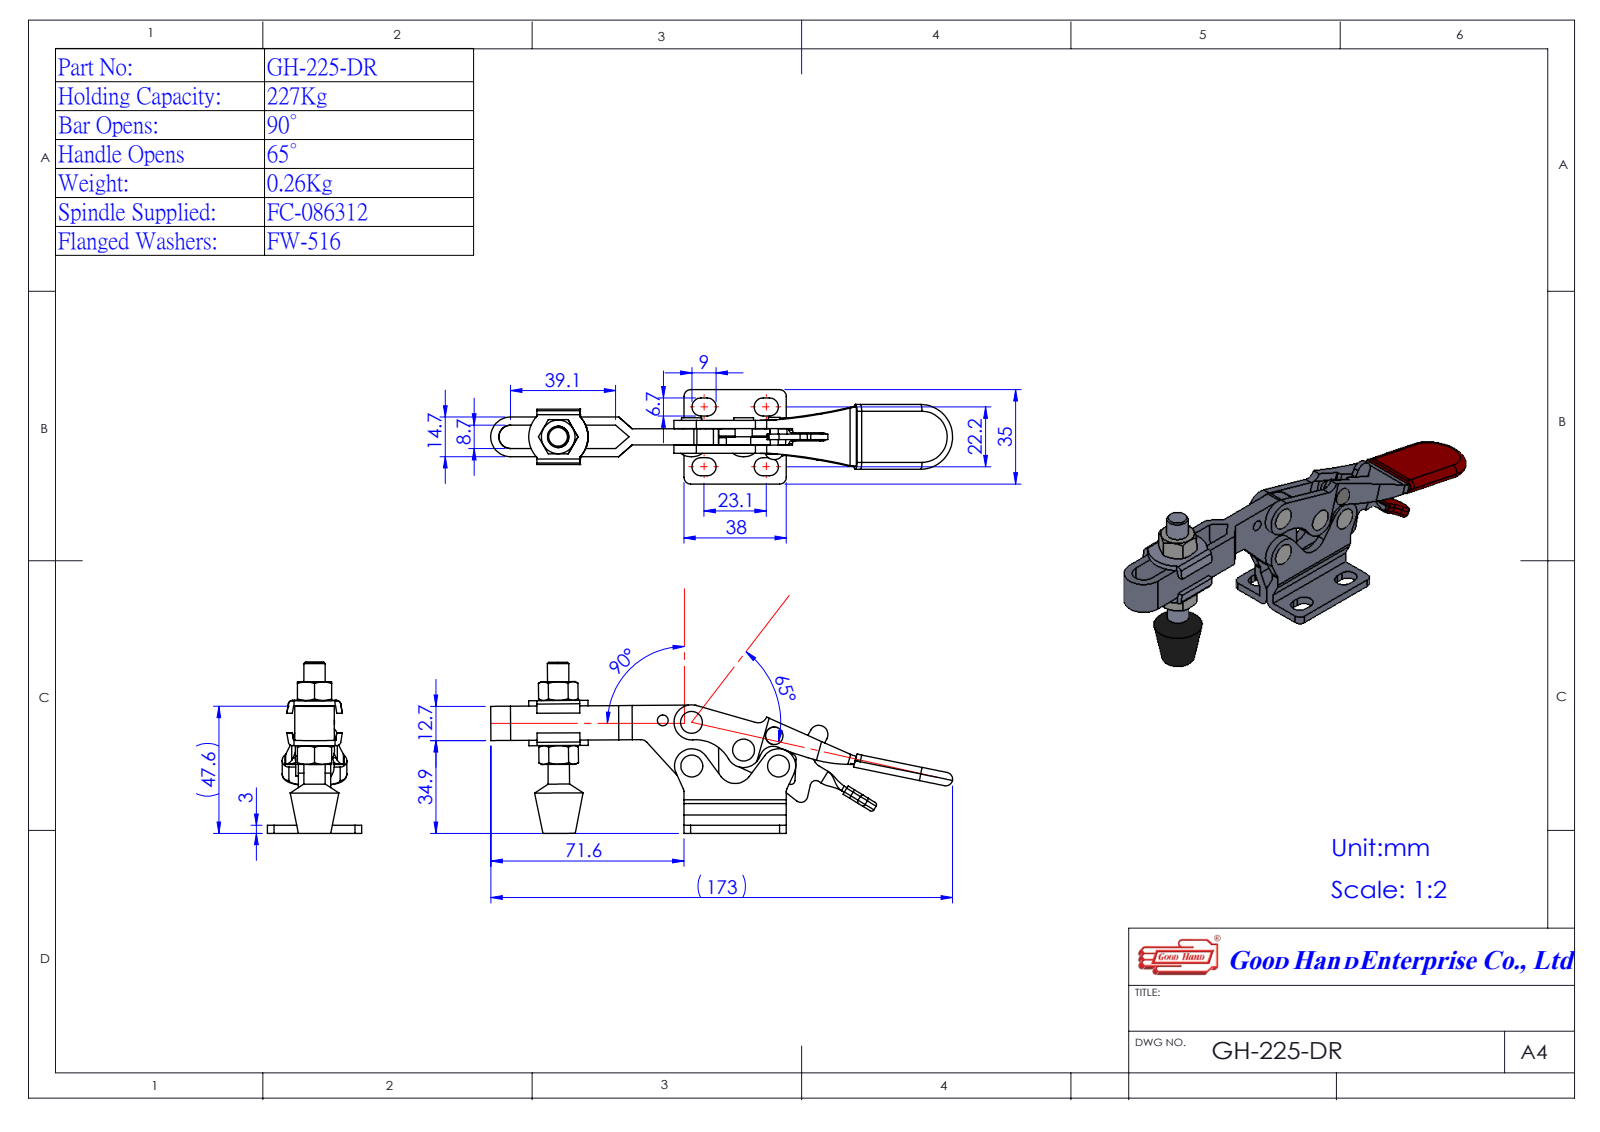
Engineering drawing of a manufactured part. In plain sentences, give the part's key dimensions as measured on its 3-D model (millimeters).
The part is named "1225D13; GH-225-D 6.35-12.2; GH-FC-56212; GH-FC56212(63) (+8 more)". Its 3-D file was written by "SolidWorks 2016 (AUTOMOTIVE_DESIGN)". It is 17 solids with 423 faces: 178 planar, 191 cylindrical and 54 other. Overall it measures 171.46 by 63.56 by 35 millimeters. Its volume is 30 007 cubic millimeters and its surface area 31 512 square millimeters. Round holes: 4 of diameter 6.35, 2 of diameter 6.3, 1 of diameter 3.1, 1 of diameter 4, 1 of diameter 7.93, 1 of diameter 8.3. Round bosses or shafts: 4 of diameter 7.35, 1 of diameter 4.4, 1 of diameter 3. Partial cylindrical surfaces (rounded edges, fillets, slot ends): 11 of radius 3, 8 of radius 3.35, 7 of radius 2, 7 of radius 2.5, 6 of radius 1, 6 of radius 1.5, 4 of radius 5, 3 of radius 4.2. The main face-to-face distances are 3, 6, 7.35, 1.35, 4.35, 10.35, 2, 1, 4, 1.25. The hole center spacings are 10.67, 11.33, 12.55, 14.25, 16.2, 20.05, 20.13, 21.9.
